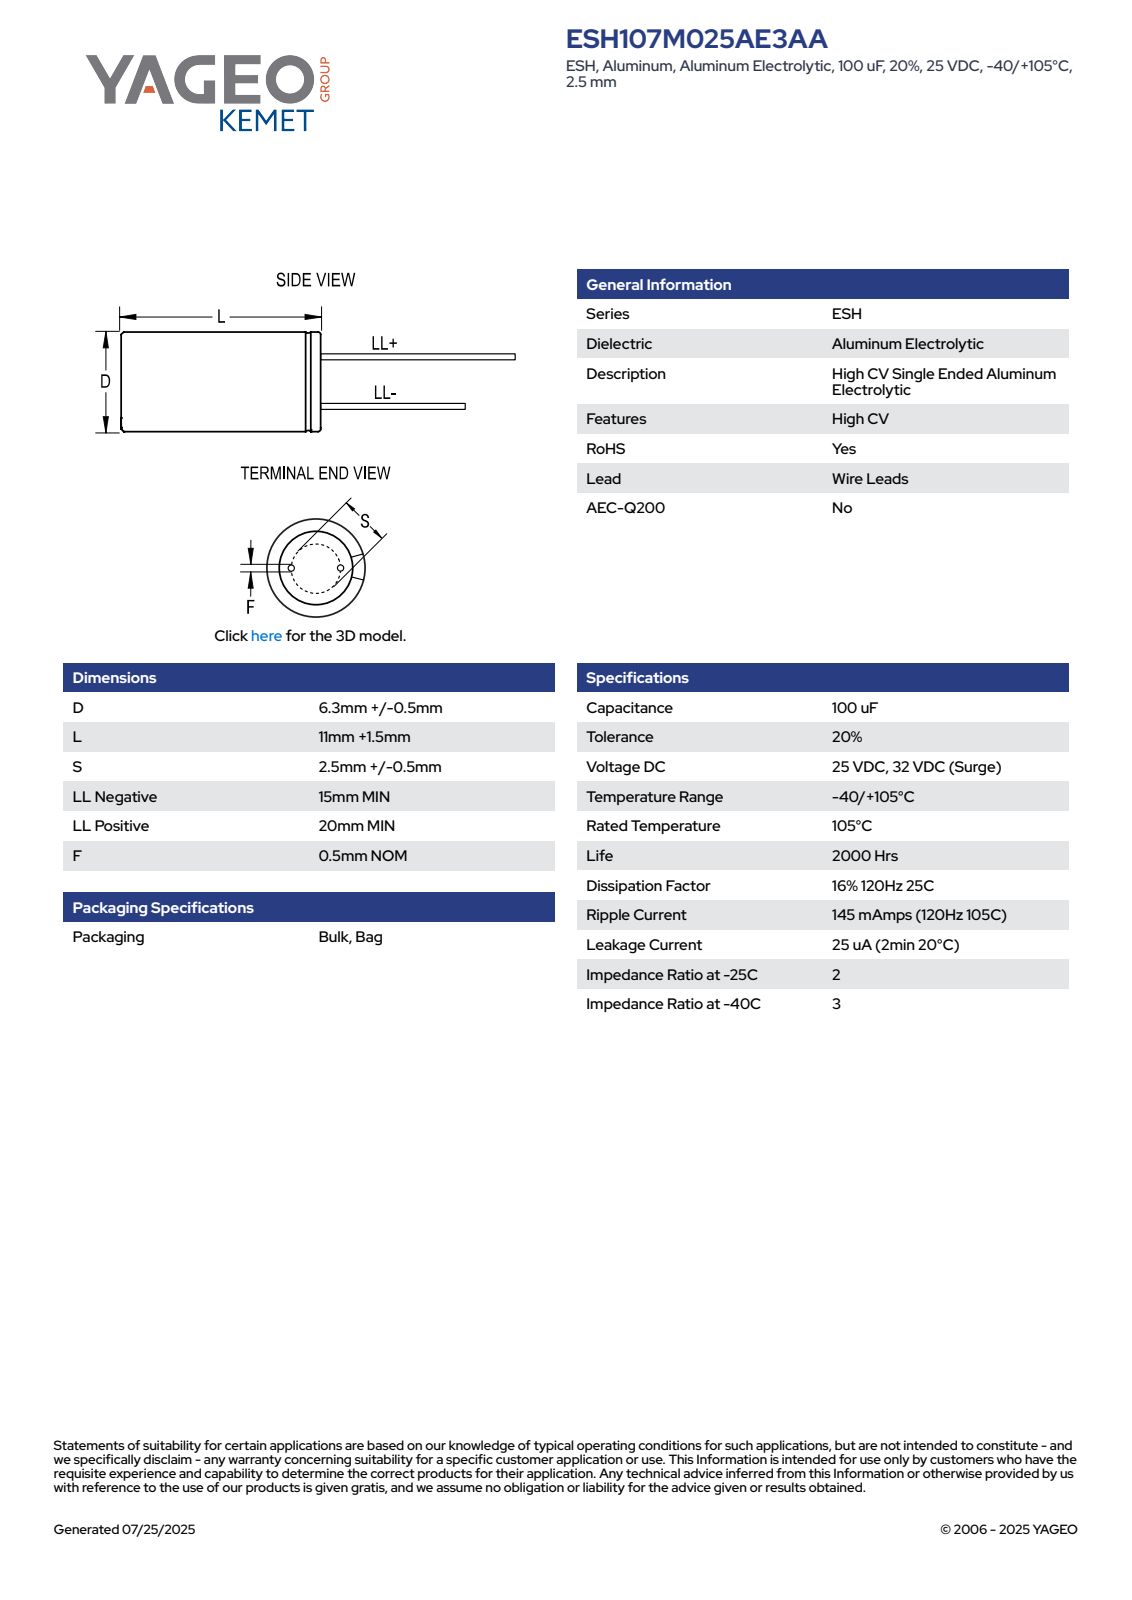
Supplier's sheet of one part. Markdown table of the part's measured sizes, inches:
| quantity | value |
| --- | --- |
| part name | CAR_KLP_6.3X11_D6.8L12.5S2.5F0.5 |
| STEP written by | SolidWorks 2014 (AUTOMOTIVE_DESIGN) |
| units | inches |
| bodies | 4 solids, 75 faces (61 planar, 8 cylindrical, 6 other) |
| overall size | 1.28 × 0.268 × 0.268 |
| volume | 0.028 in³ |
| surface area | 0.626 in² |
| round bosses / shafts (diameter × count) | 0.02 × 2, 0.268 × 1 |
| main face-to-face distances | 0.492, 0.493, 1.083, 1.28, 1.083, 1.28, 0.591, 0.787, 0.197, 0.036 |
